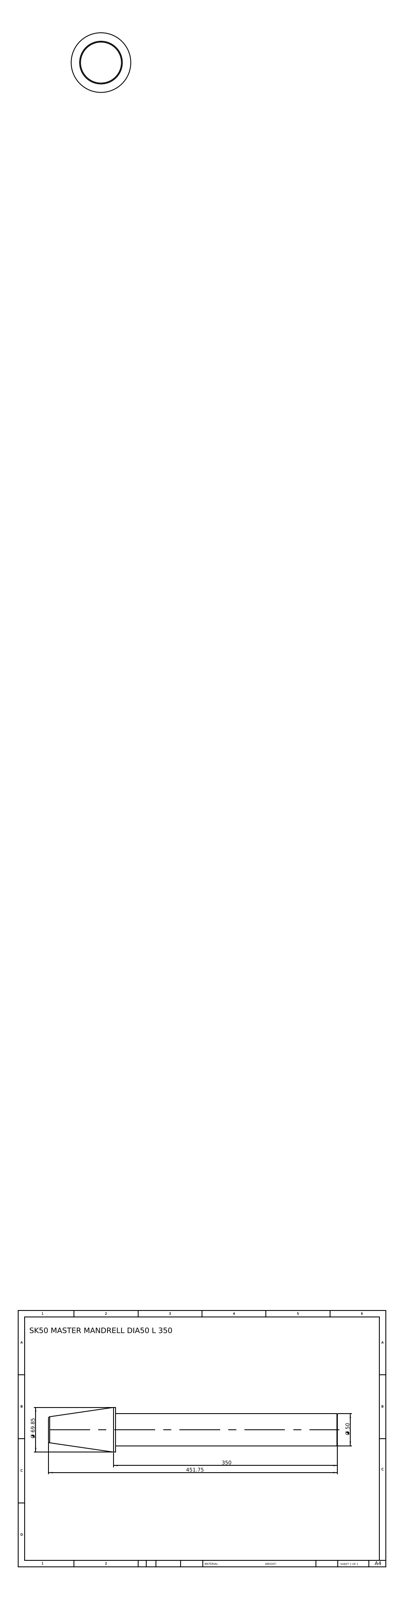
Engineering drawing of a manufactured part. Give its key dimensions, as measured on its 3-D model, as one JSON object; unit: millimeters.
{"part_name": "SK50 MASTER MANDRELL DIA50 L350", "step_written_by": "SolidWorks 2014 (CONFIG_CONTROL_DESIGN)", "units": "millimeters", "bodies": {"solids": 1, "faces": 13, "planar": 3, "cylindrical": 4, "other": 6}, "overall_size": [451.75, 69.85, 69.85], "volume_mm3": 940723, "surface_area_mm2": 77857, "round_bosses_or_shafts": [[69.85, 1], [50, 1]], "face_to_face_distances": [346.8, 104.95, 451.75]}
